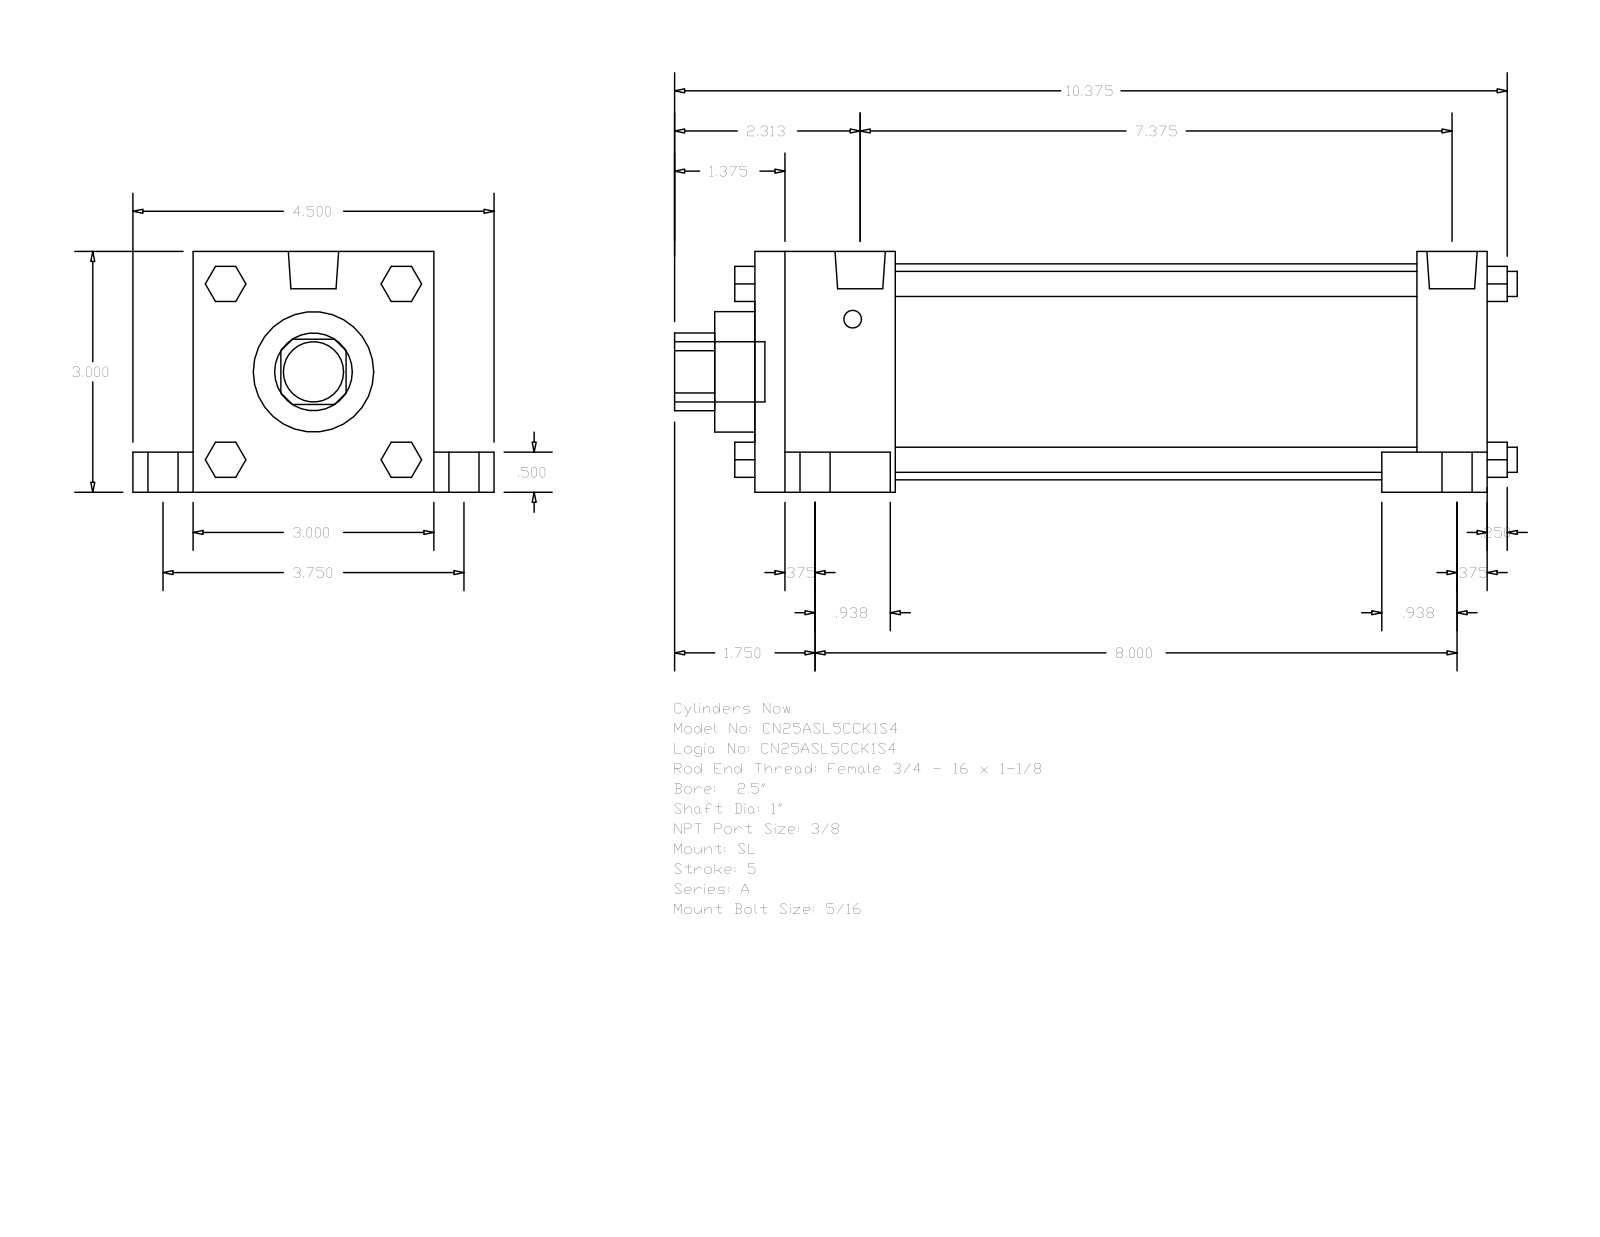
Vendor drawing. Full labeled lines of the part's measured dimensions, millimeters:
Part name (STEP PRODUCT): A_SL__0250_1
STEP written by: GSSL Pune (CONFIG_CONTROL_DESIGN)
Units: millimetres
Bodies: 0 solids, 148 faces (112 planar, 36 cylindrical, 0 other)
Overall size (bounding box): 266.7 × 114.3 × 76.2
Round holes (diameter × count): ⌀25.4 ×1, ⌀38.1 ×1, ⌀68.33 ×1
Round bosses / shafts (diameter × count): ⌀15.88 ×4, ⌀9.53 ×4, ⌀7.94 ×4, ⌀5.56 ×4, ⌀15.93 ×2, ⌀19.05 ×1
Partial cylindrical surfaces — rounded edges, fillets, slot ends (radius × count): R12.29 ×1
Main face-to-face distances: 76.2, 231.78, 12.7, 44.45, 187.33, 209.55, 165.1, 22.23, 19.05, 63.5
